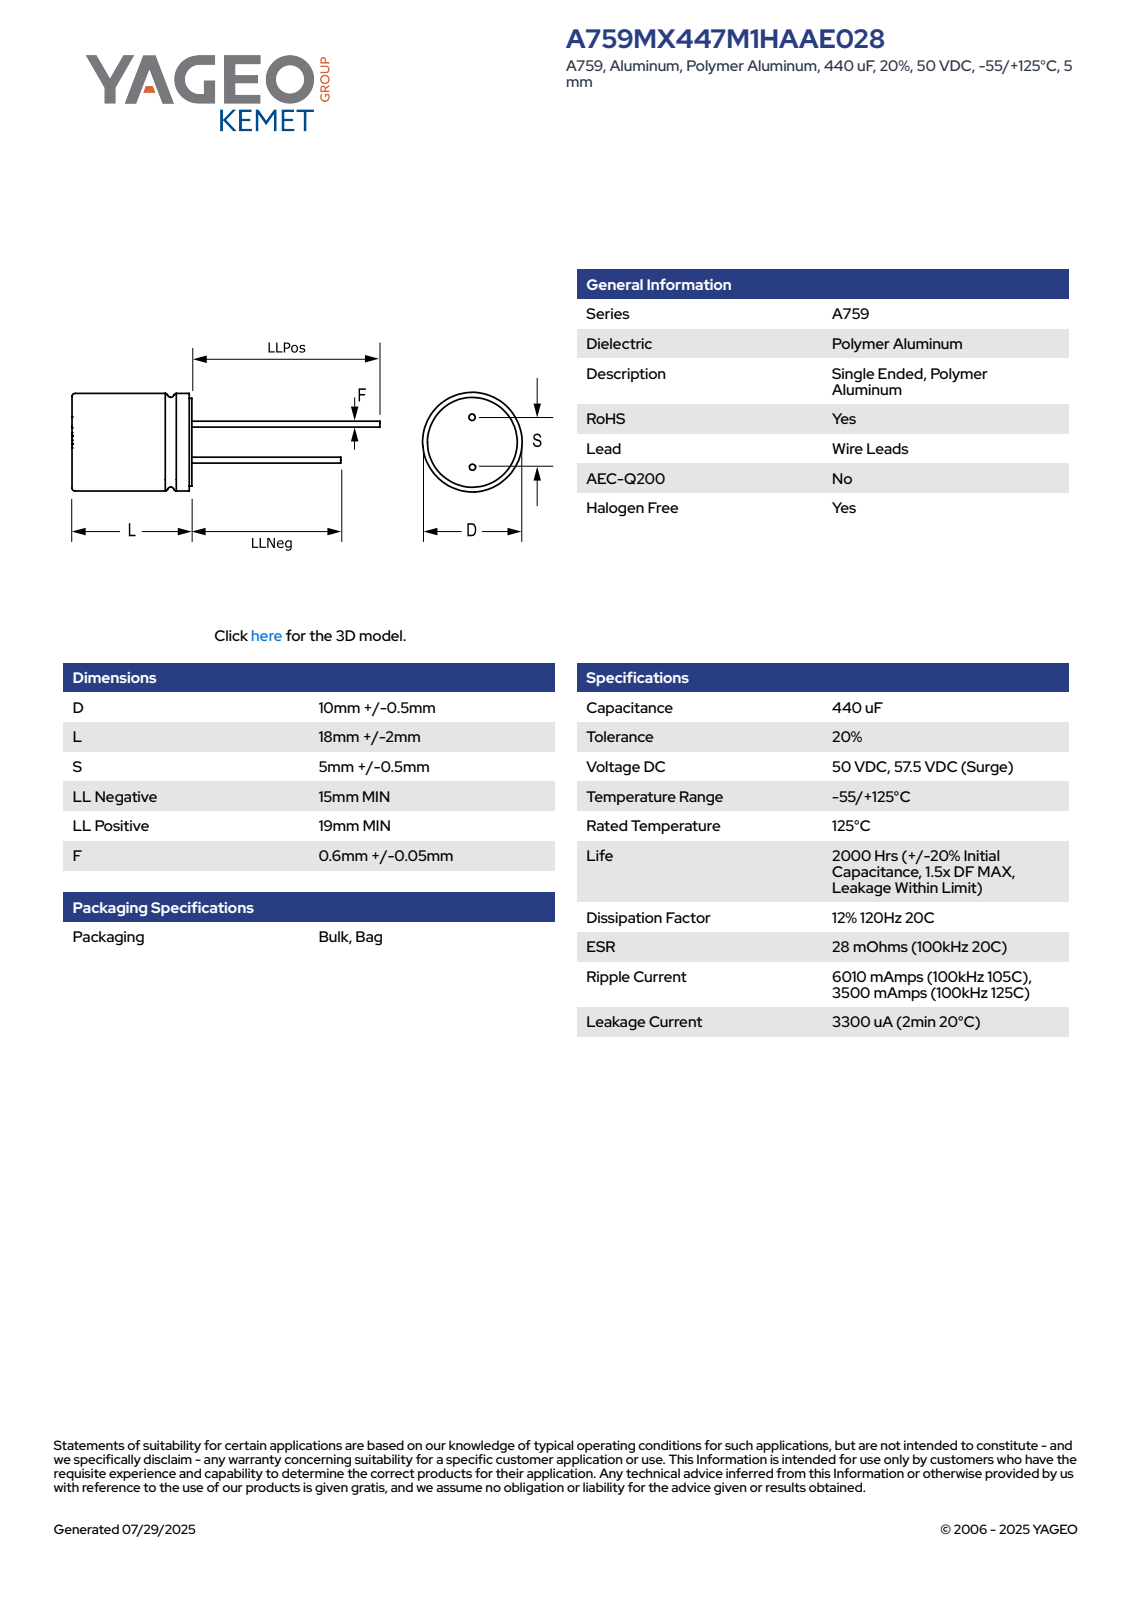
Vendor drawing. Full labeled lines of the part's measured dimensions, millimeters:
Part name (STEP PRODUCT): CAR_KP_10X18_D10.5L20S5F0.65
STEP written by: SolidWorks 2014 (AUTOMOTIVE_DESIGN)
Units: millimetres
Bodies: 4 solids, 75 faces (61 planar, 8 cylindrical, 6 other)
Overall size (bounding box): 39.01 × 10.5 × 10.5
Volume: 1 724 mm³ · Surface area: 926 mm²
Round bosses / shafts (diameter × count): ⌀0.65 ×2, ⌀10.5 ×1
Main face-to-face distances: 20, 20.01, 35.01, 39.01, 35, 39, 15, 19, 4, 1.15
